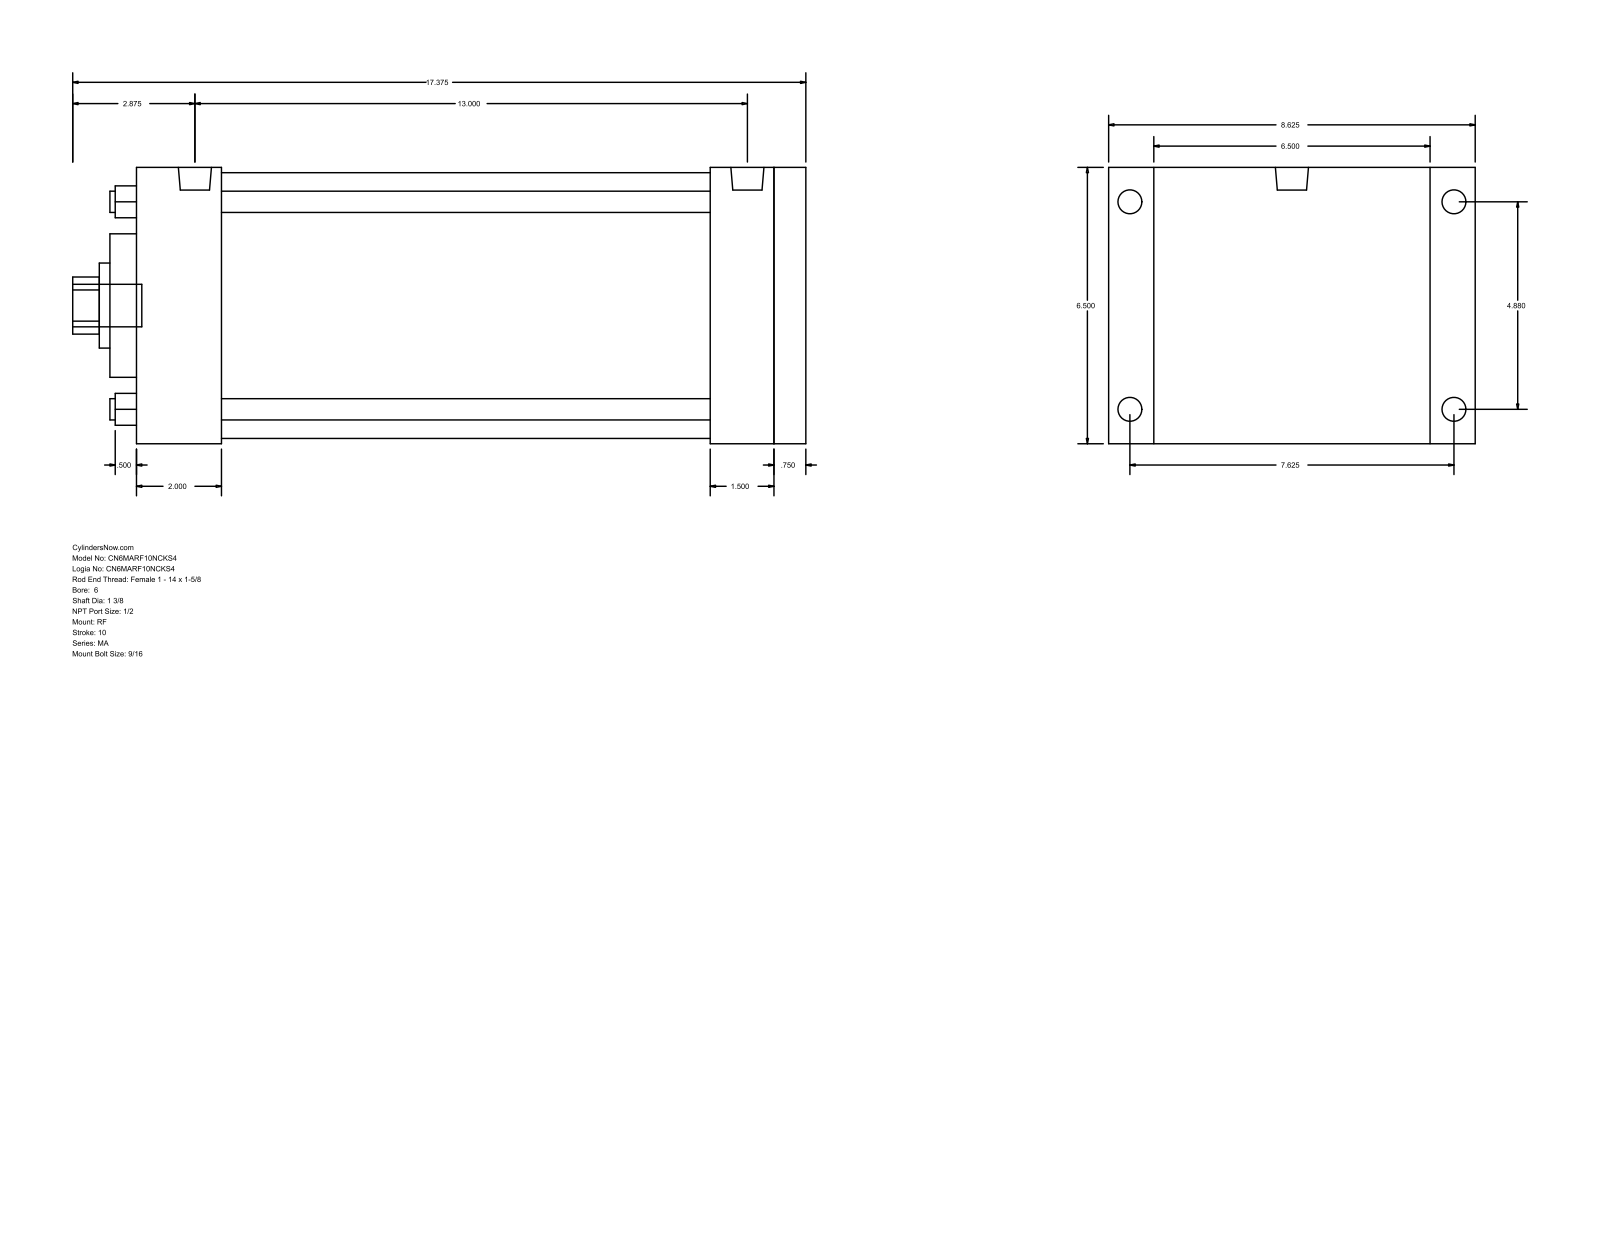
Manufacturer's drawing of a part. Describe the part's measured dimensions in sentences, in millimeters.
The part is named "MA_RF__0600_1.375". Its 3-D file was written by "GSSL Pune (CONFIG_CONTROL_DESIGN)". It is 0 solids with 94 faces: 65 planar, 29 cylindrical and 0 other. Overall it measures 441.32 by 219.07 by 165.1 millimeters. Round holes: 4 of diameter 12.7, 1 of diameter 34.92, 1 of diameter 50.8, 1 of diameter 85.72, 1 of diameter 158.75. Round bosses or shafts: 4 of diameter 17.46, 4 of diameter 14.29, 2 of diameter 19.77, 1 of diameter 25.4. Partial cylindrical surfaces (rounded edges, fillets, slot ends): 1 of radius 17.06. The main face-to-face distances are 165.1, 403.22, 19.05, 384.17, 50.8, 333.37, 352.42, 346.08, 295.28, 38.09. The hole center spacings are 87.65, 123.96, 175.31.
